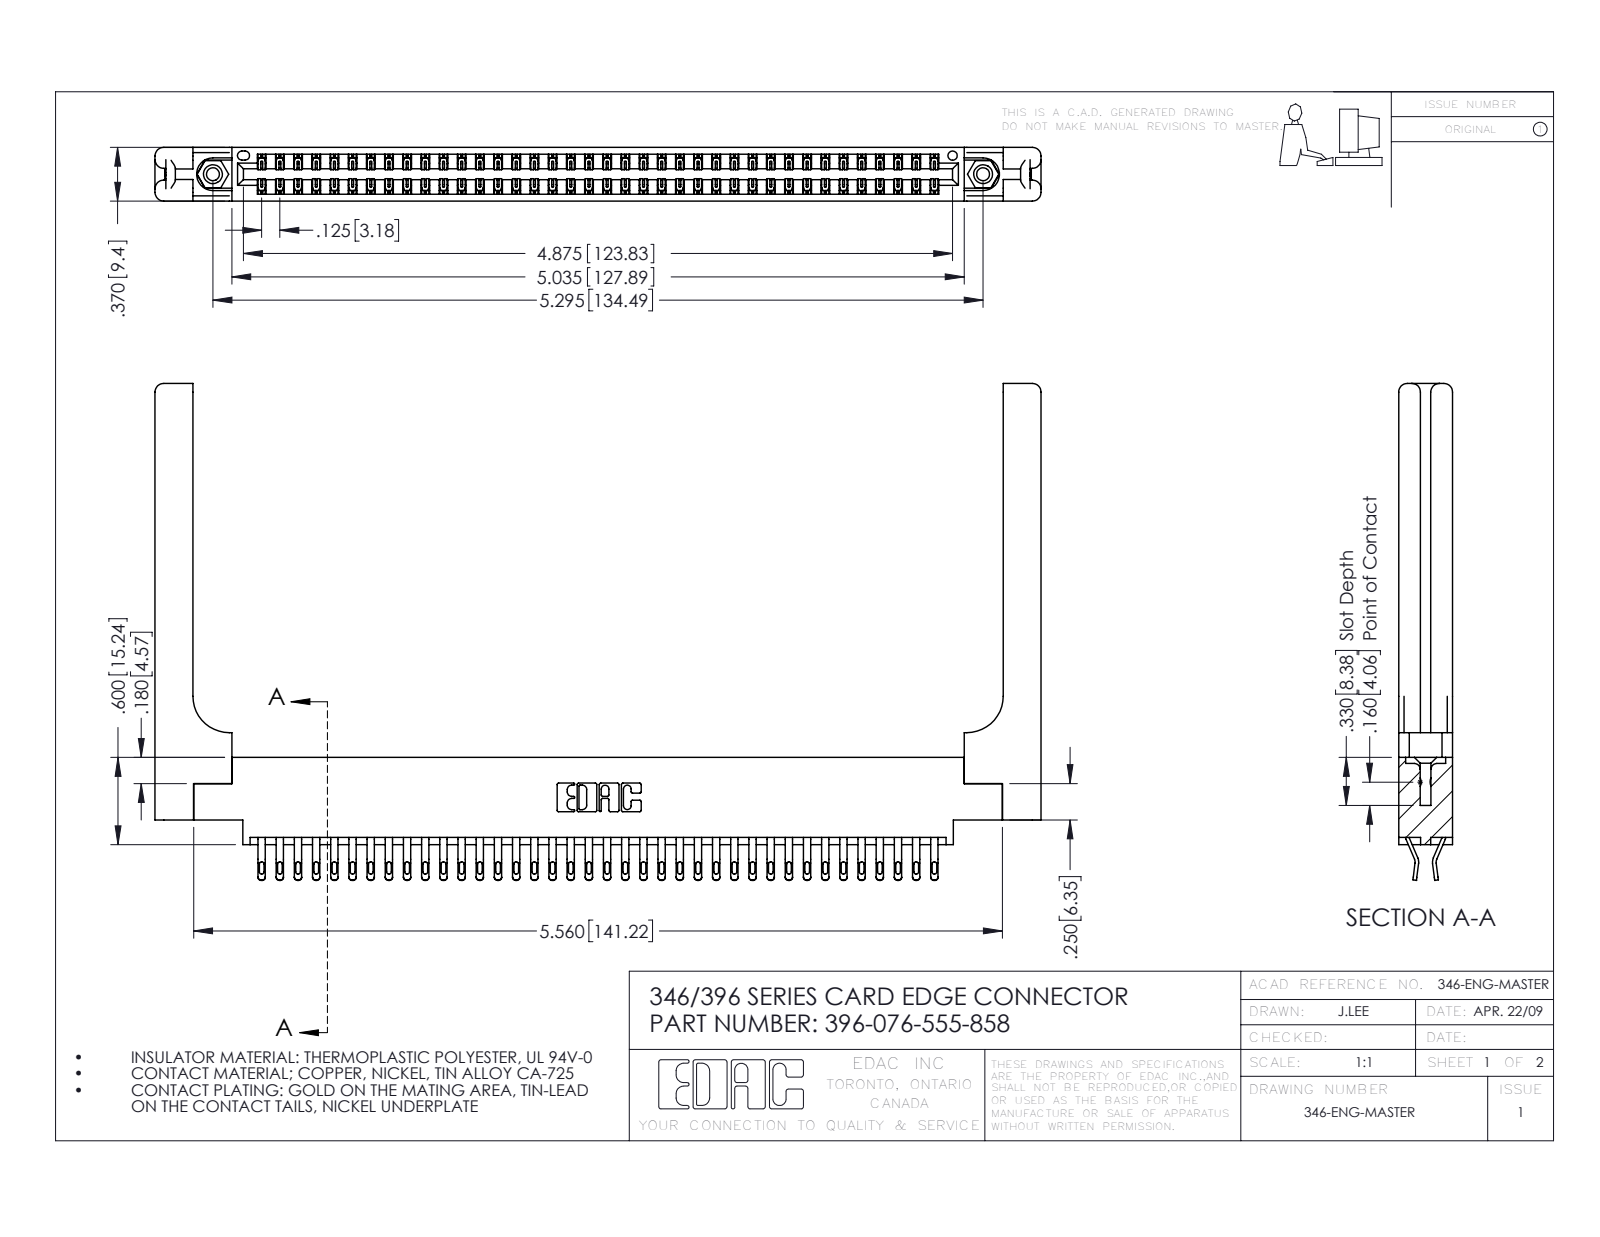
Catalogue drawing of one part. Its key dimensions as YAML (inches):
part_name: "346-220-058_345-220-058; 346 Part_0.170 Offset - 0.156 Dia-TH; 345-292-001_555 Tail; 345-250-001_345-250-001-102 (+1 more)"
step_written_by: "SolidWorks 2016 (CONFIG_CONTROL_DESIGN)"
units: inches
bodies: {solids: 81, faces: 4790, planar: 2736, cylindrical: 1994, other: 60}
overall_size: [6.091, 3.415, 0.37]
volume: 1.38
surface_area: 41.32
round_holes:
  - {diameter: 0.089, count: 2}
  - {diameter: 0.125, count: 2}
  - {diameter: 0.156, count: 2}
  - {diameter: 0.064, count: 1}
round_bosses_or_shafts:
  - {diameter: 0.155, count: 2}
partial_cylinders:
  - {radius: 0.016, count: 152}
  - {radius: 0.02, count: 152}
  - {radius: 0.006, count: 114}
  - {radius: 0.01, count: 22}
  - {radius: 0.06, count: 16}
  - {radius: 0.007, count: 6}
  - {radius: 0.031, count: 6}
  - {radius: 0.026, count: 3}
face_to_face_distances: [0.37, 0.048, 0.322, 0.072, 0.148, 0.15, 0.25, 0.025, 0.298, 0.275]
hole_center_spacings: [0.246, 5.086, 5.295]
